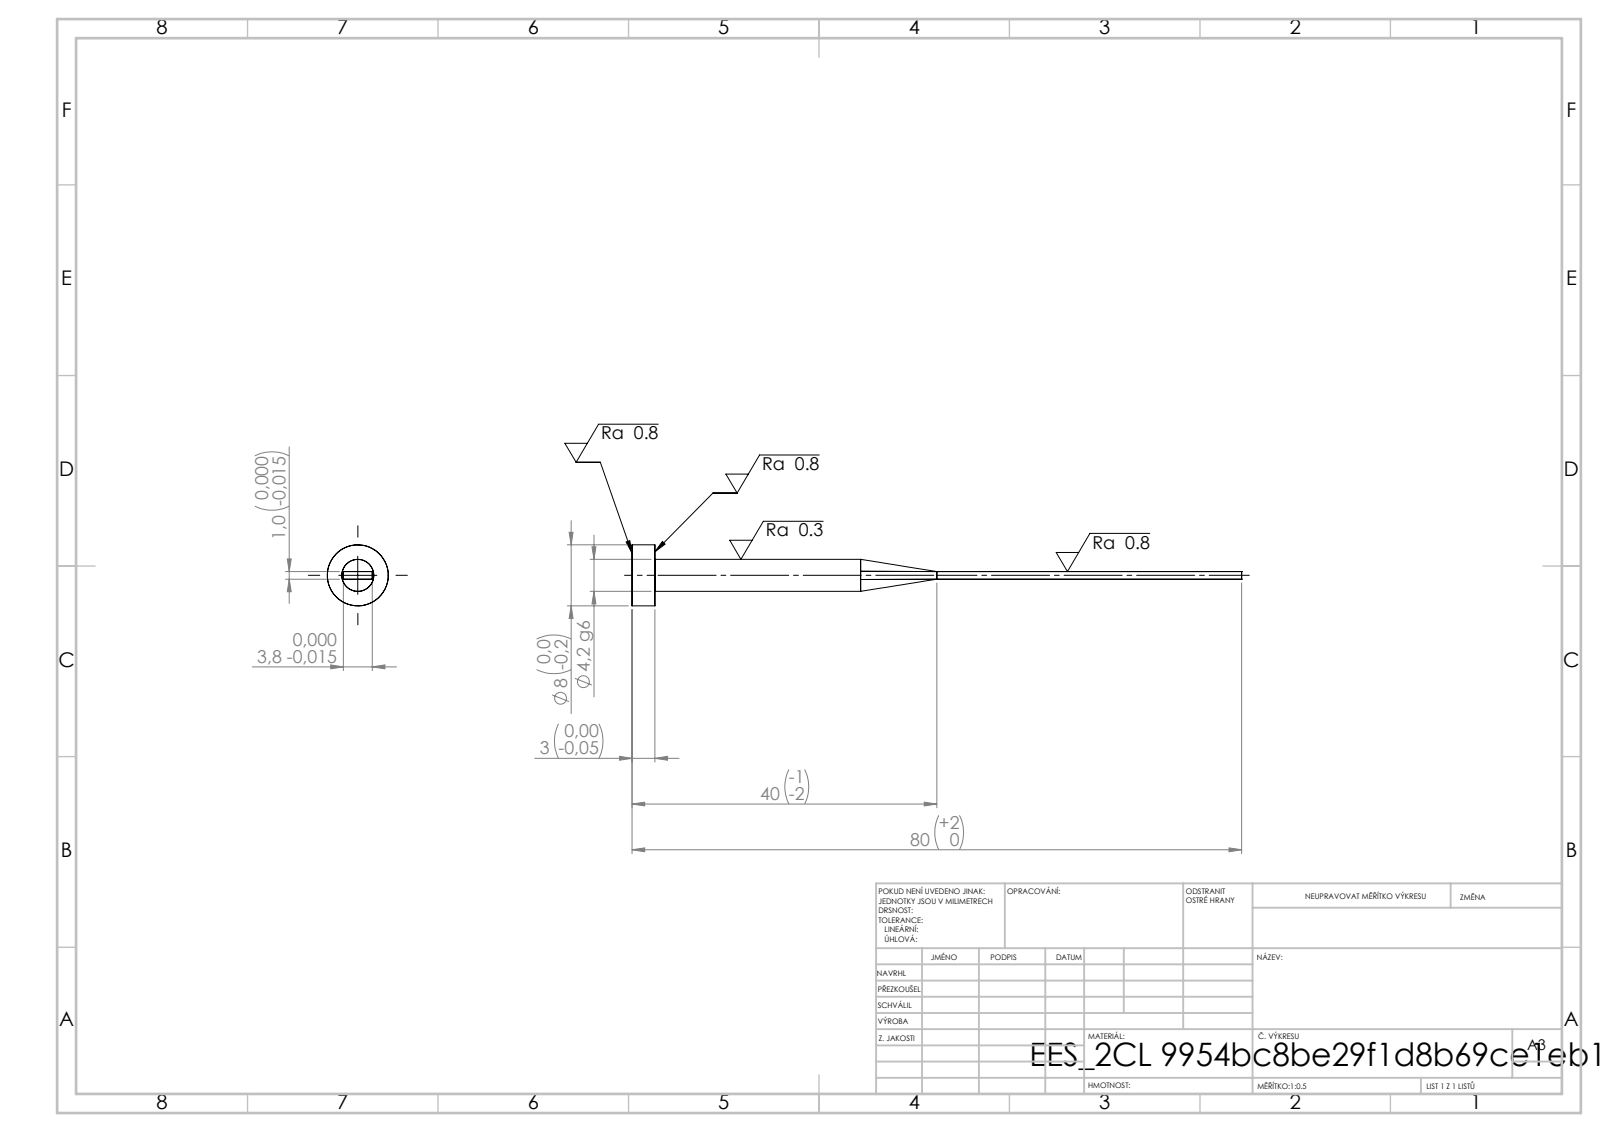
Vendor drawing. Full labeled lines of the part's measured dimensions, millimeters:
STEP written by: SolidWorks 2019 (CONFIG_CONTROL_DESIGN)
Units: millimetres
Bodies: 1 solid, 15 faces (7 planar, 4 cylindrical, 4 other)
Overall size (bounding box): 80 × 8 × 8
Volume: 761 mm³ · Surface area: 1 016 mm²
Round bosses / shafts (diameter × count): ⌀8 ×1, ⌀4.2 ×1
Main face-to-face distances: 1, 3.8, 3, 80, 77
